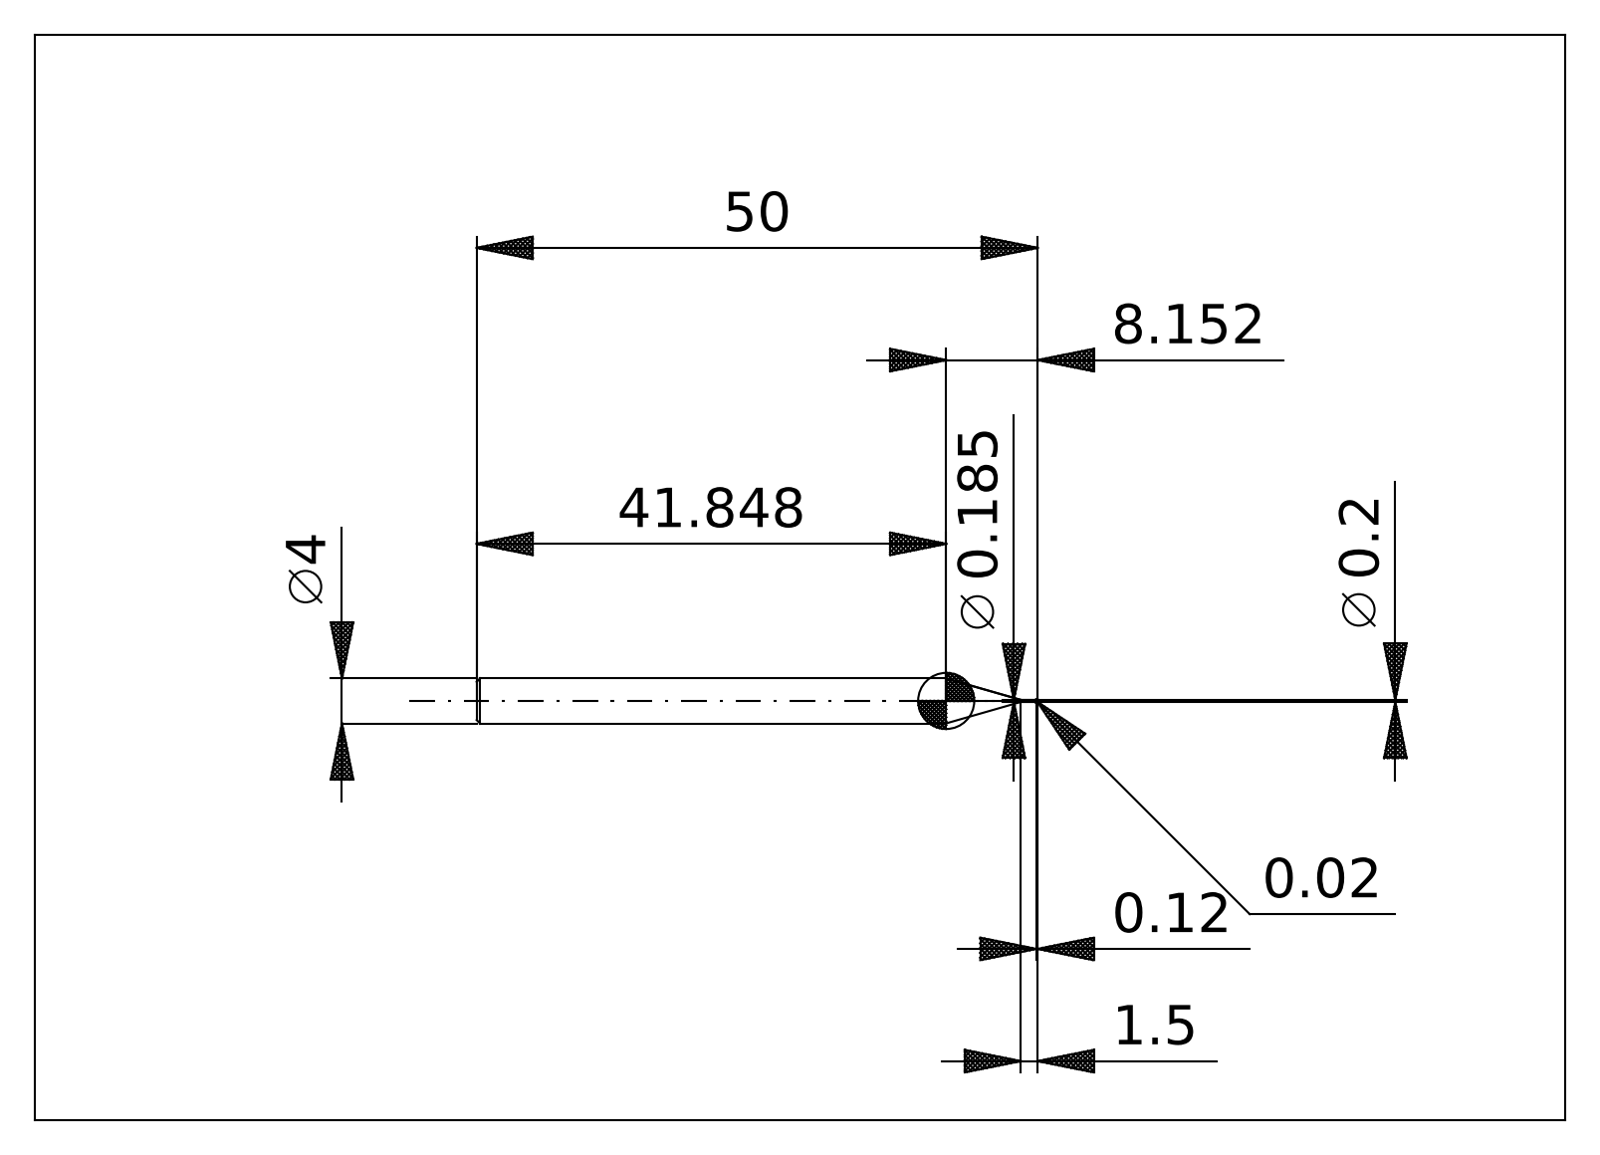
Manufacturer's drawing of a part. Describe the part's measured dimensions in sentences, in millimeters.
Its 3-D file was written by "ACIS (automotive_design)". It is 2 solids with 26 faces: 6 planar, 8 cylindrical and 12 other. Overall it measures 50 by 4 by 4 millimeters. Its volume is 555 cubic millimeters and its surface area 583 square millimeters. Round bosses or shafts: 1 of diameter 4. The main face-to-face distances are 50, 49.97, 49.88, 8.15, 8.12, 8.03, 41.85.
